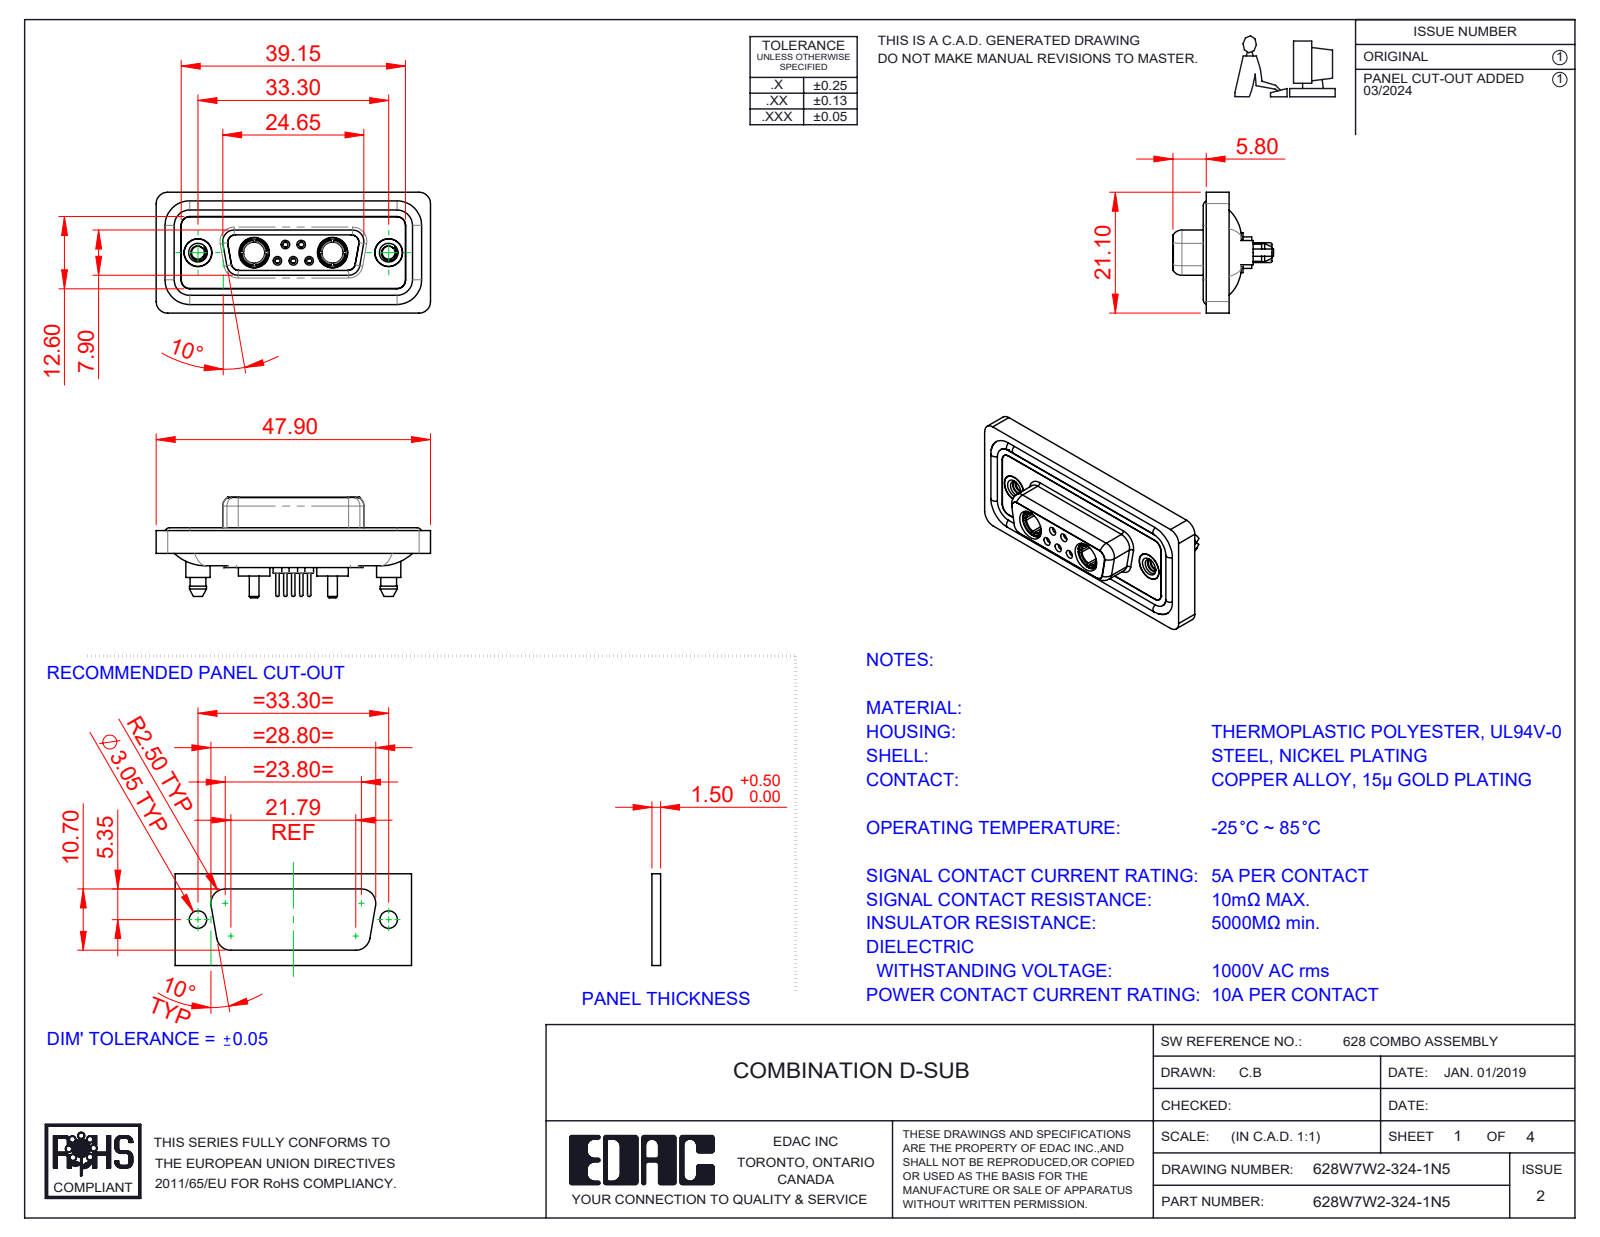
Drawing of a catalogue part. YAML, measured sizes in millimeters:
part_name: "628Combo Shell Front_15 Contacts; 628Combo Waterproof Housing_15 Contacts; 628Combo Shell Rear_15 Contacts; 628Combo Threaded Boardlock_5 (+5 more)"
step_written_by: "SolidWorks 2023 (CONFIG_CONTROL_DESIGN)"
units: millimeters
bodies: {solids: 16, faces: 859, planar: 254, cylindrical: 361, other: 244}
overall_size: [47.9, 21.1, 17.55]
volume: 6181
surface_area: 10193
round_holes:
  - {diameter: 0.9, count: 5}
  - {diameter: 1.1, count: 5}
  - {diameter: 1.5, count: 5}
  - {diameter: 2, count: 5}
  - {diameter: 4.85, count: 4}
  - {diameter: 1.6, count: 3}
  - {diameter: 1.7, count: 2}
  - {diameter: 2.26, count: 2}
  - {diameter: 3.7, count: 2}
  - {diameter: 4, count: 2}
  - {diameter: 4.05, count: 2}
  - {diameter: 5, count: 2}
round_bosses_or_shafts:
  - {diameter: 1.6, count: 6}
  - {diameter: 2.2, count: 5}
  - {diameter: 0.6, count: 5}
  - {diameter: 5.5, count: 2}
  - {diameter: 5.4, count: 2}
  - {diameter: 5.2, count: 2}
  - {diameter: 4.96, count: 2}
  - {diameter: 4.95, count: 2}
partial_cylinders:
  - {radius: 1.5, count: 24}
  - {radius: 2, count: 20}
  - {radius: 1.35, count: 12}
  - {radius: 1.6, count: 10}
  - {radius: 0.25, count: 4}
  - {radius: 0.5, count: 4}
  - {radius: 0.6, count: 4}
  - {radius: 0.65, count: 4}
face_to_face_distances: [0.4, 1.8, 1.6, 0.5, 2.9, 1.1, 7.45, 5.65, 6.6, 7.05]
hole_center_spacings: [3.16, 2.77, 9.8, 23.5, 4.31, 4.33, 5.03, 5.04]
